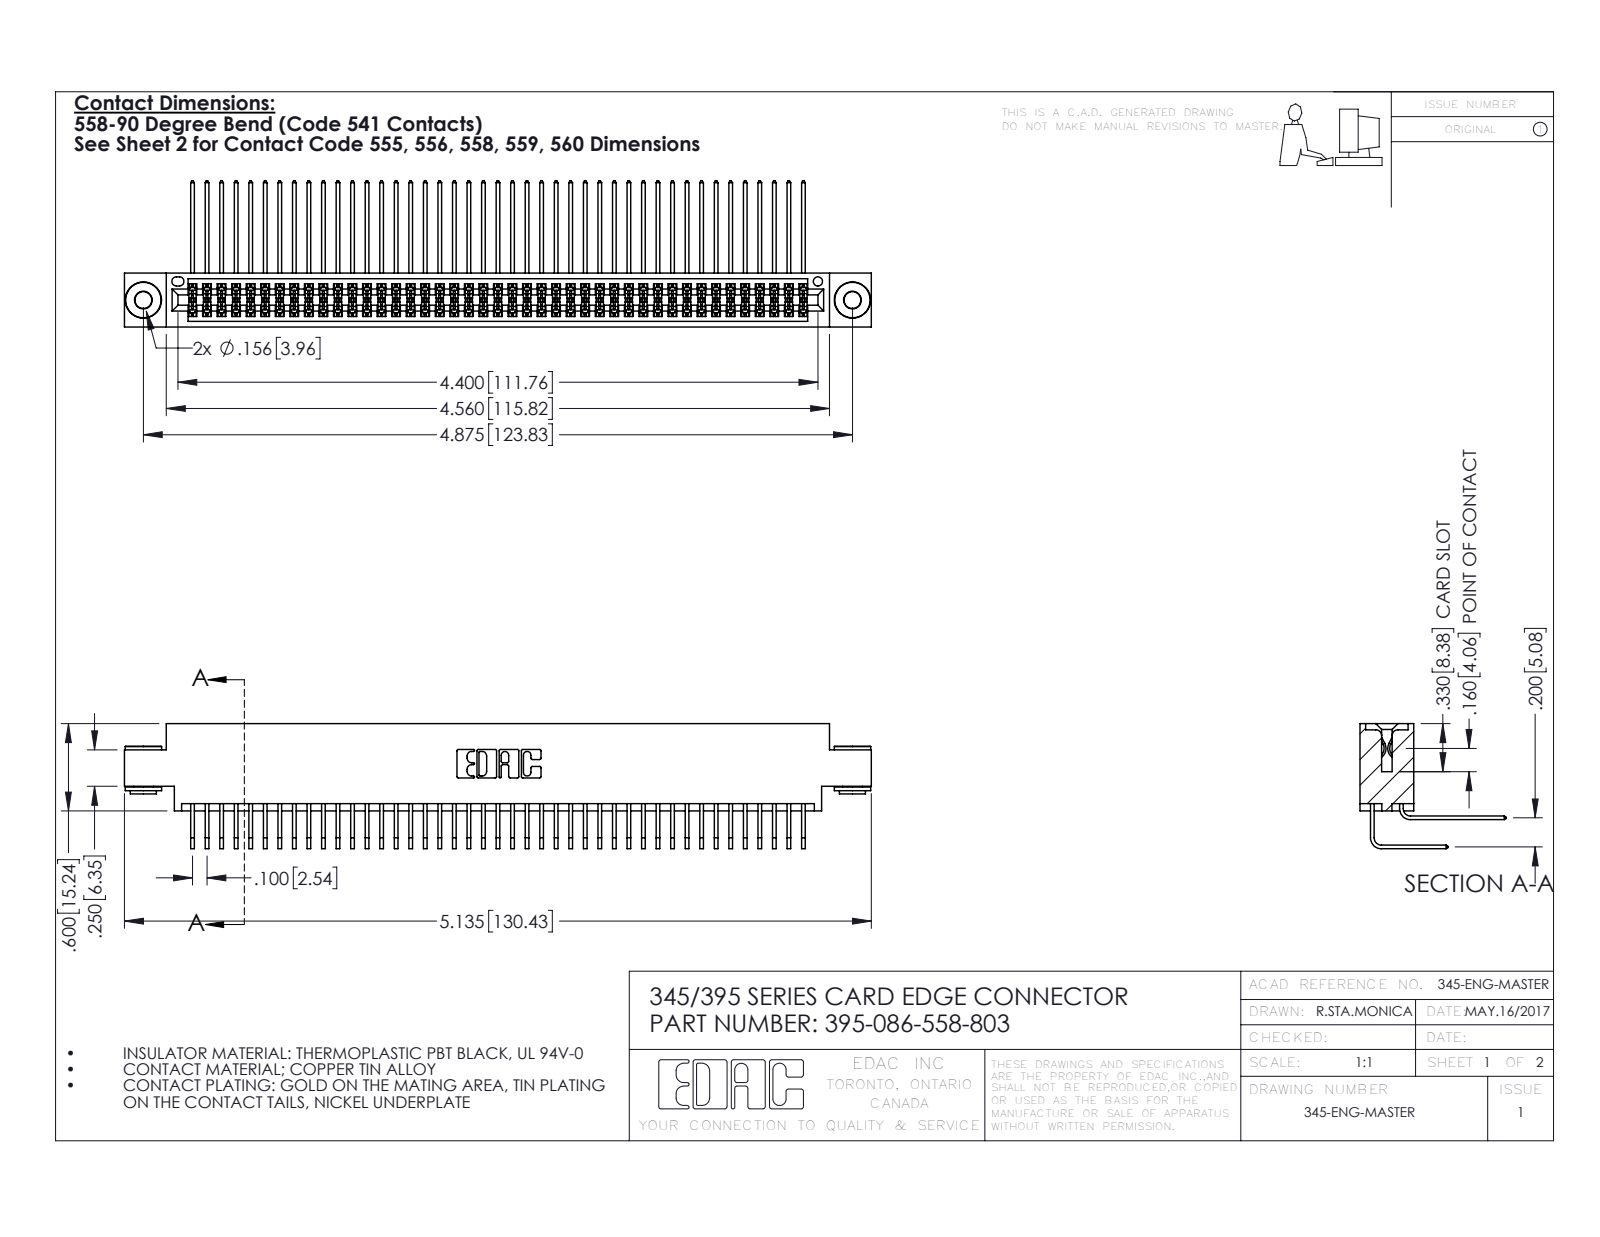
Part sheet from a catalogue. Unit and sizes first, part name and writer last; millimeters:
Units: millimetres
Overall size (bounding box): 130.4 × 25.5 × 21.8
Round holes (diameter × count): ⌀2.9 ×2, ⌀4 ×2, ⌀1.6 ×1
Round bosses / shafts (diameter × count): ⌀6.4 ×2, ⌀4.6 ×2, ⌀3.5 ×2
Partial cylindrical surfaces — rounded edges, fillets, slot ends (radius × count): R0.2 ×130, R0.3 ×22, R0.2 ×6, R0.8 ×6, R0.7 ×3, R0.4 ×2, R0.5 ×2, R0.6 ×2
Main face-to-face distances: 1.8, 7.6, 5.1, 9.4, 2.5, 6.9, 0.6, 5.7, 4.4, 0.6
Hole centre spacings: 6.9, 117.8, 123.8
Volume: 13 100 mm³ · Surface area: 22 040 mm²
Bodies: 89 solids, 4640 faces (3104 planar, 1528 cylindrical, 8 other)
Part name (STEP PRODUCT): 345-292-001_558 559 Tail - 1; 345 Part_0.170 Offset - 0.156 Dia-TH; 395-086-558-803; 345-250-002_345-250-002-102 (+1 more)
STEP written by: SolidWorks 2016 (CONFIG_CONTROL_DESIGN)
